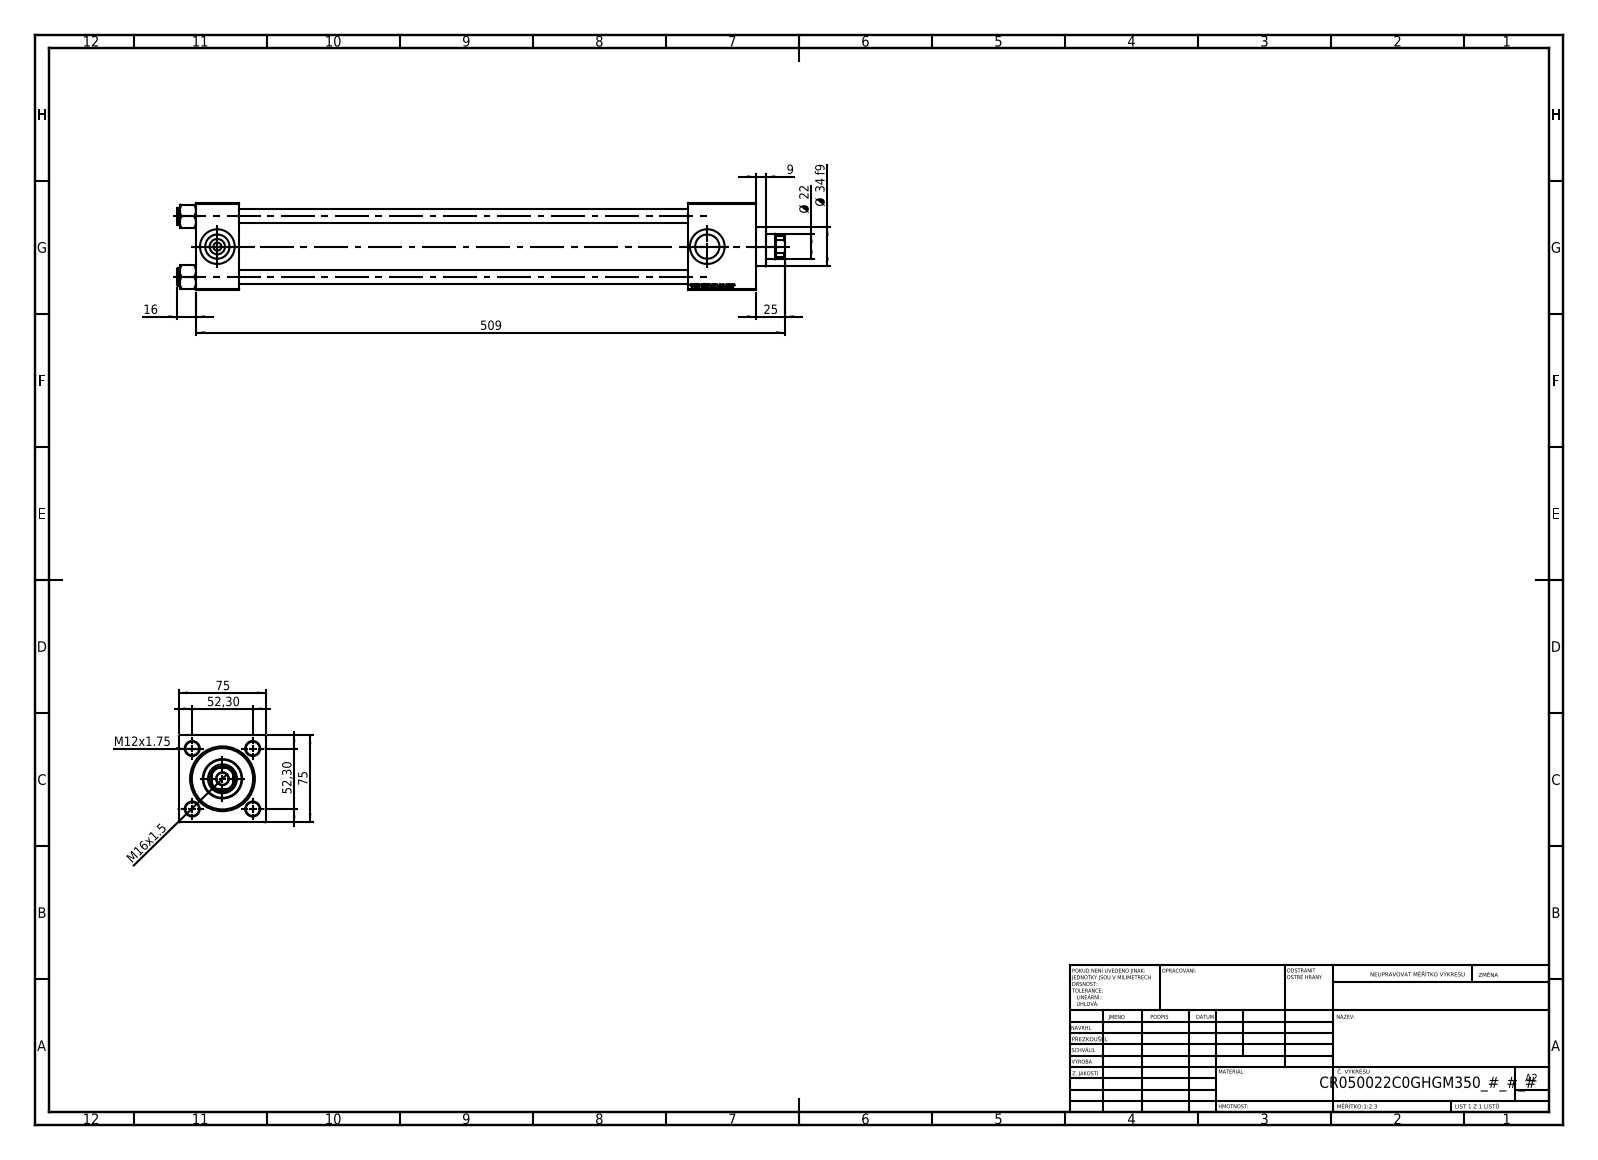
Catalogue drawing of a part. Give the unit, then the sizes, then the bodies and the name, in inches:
Units: inches
Overall size (bounding box): 20.669 × 2.974 × 2.953
Round holes (diameter × count): ⌀0.472 ×4, ⌀0.276 ×2, ⌀0.825 ×2, ⌀1.181 ×2, ⌀0.413 ×1, ⌀0.866 ×1, ⌀0.984 ×1, ⌀1.614 ×1, ⌀1.969 ×1, ⌀2.087 ×1
Round bosses / shafts (diameter × count): ⌀0.591 ×4, ⌀2.205 ×1, ⌀1.339 ×1
Partial cylindrical surfaces — rounded edges, fillets, slot ends (radius × count): R0.413 ×1
Main face-to-face distances: 2.953, 1.457, 19.055, 17.598, 16.732, 15.276, 2.323, 17.925, 16.469, 1.193
Hole centre spacings: 1.456, 2.059, 2.912, 16.673
Volume: 66.94 in³ · Surface area: 511.1 in²
Bodies: 11 solids, 1148 faces (526 planar, 86 cylindrical, 536 other)
Part name (STEP PRODUCT): NUT_M5_C; V215CR_C_Body; V215CR_VCP_C; V215_VC_A (+1 more)
STEP written by: SolidWorks 2019 (CONFIG_CONTROL_DESIGN)
